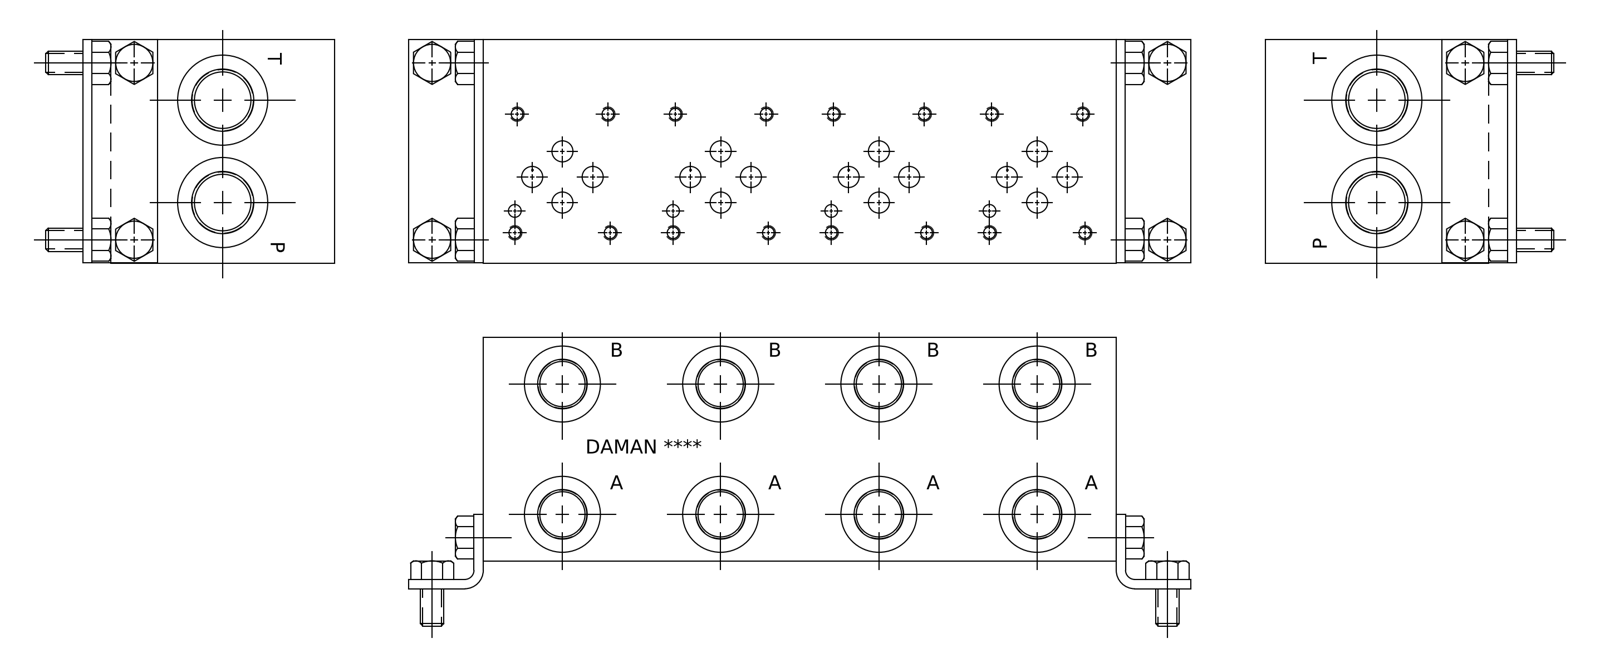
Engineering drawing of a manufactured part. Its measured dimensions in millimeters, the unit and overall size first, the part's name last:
Units: millimetres
Overall size (bounding box): 215.9 × 76.2 × 76.2
Round holes (diameter × count): ⌀4.22 ×16, ⌀5 ×16, ⌀7.14 ×12, ⌀14.3 ×8, ⌀15.06 ×8, ⌀16.76 ×8, ⌀25.93 ×8, ⌀3.96 ×4, ⌀6.35 ×4, ⌀6.76 ×2, ⌀8 ×2, ⌀15.88 ×2
Main face-to-face distances: 76.2, 215.9, 0.79, 75.41, 215.11, 214.32, 12.98, 12.19, 63.22, 16.59
Hole centre spacings: 107.95, 53.98, 53.97, 19.95, 22.05, 33.55, 40.49, 51.45
Volume: 1 173 000 mm³ · Surface area: 100 521 mm²
Bodies: 1 solid, 749 faces (413 planar, 108 cylindrical, 228 other)
Part name (STEP PRODUCT): Part_DD03P042B_3D
STEP written by: Autodesk Inventor 2019 (AUTOMOTIVE_DESIGN)
